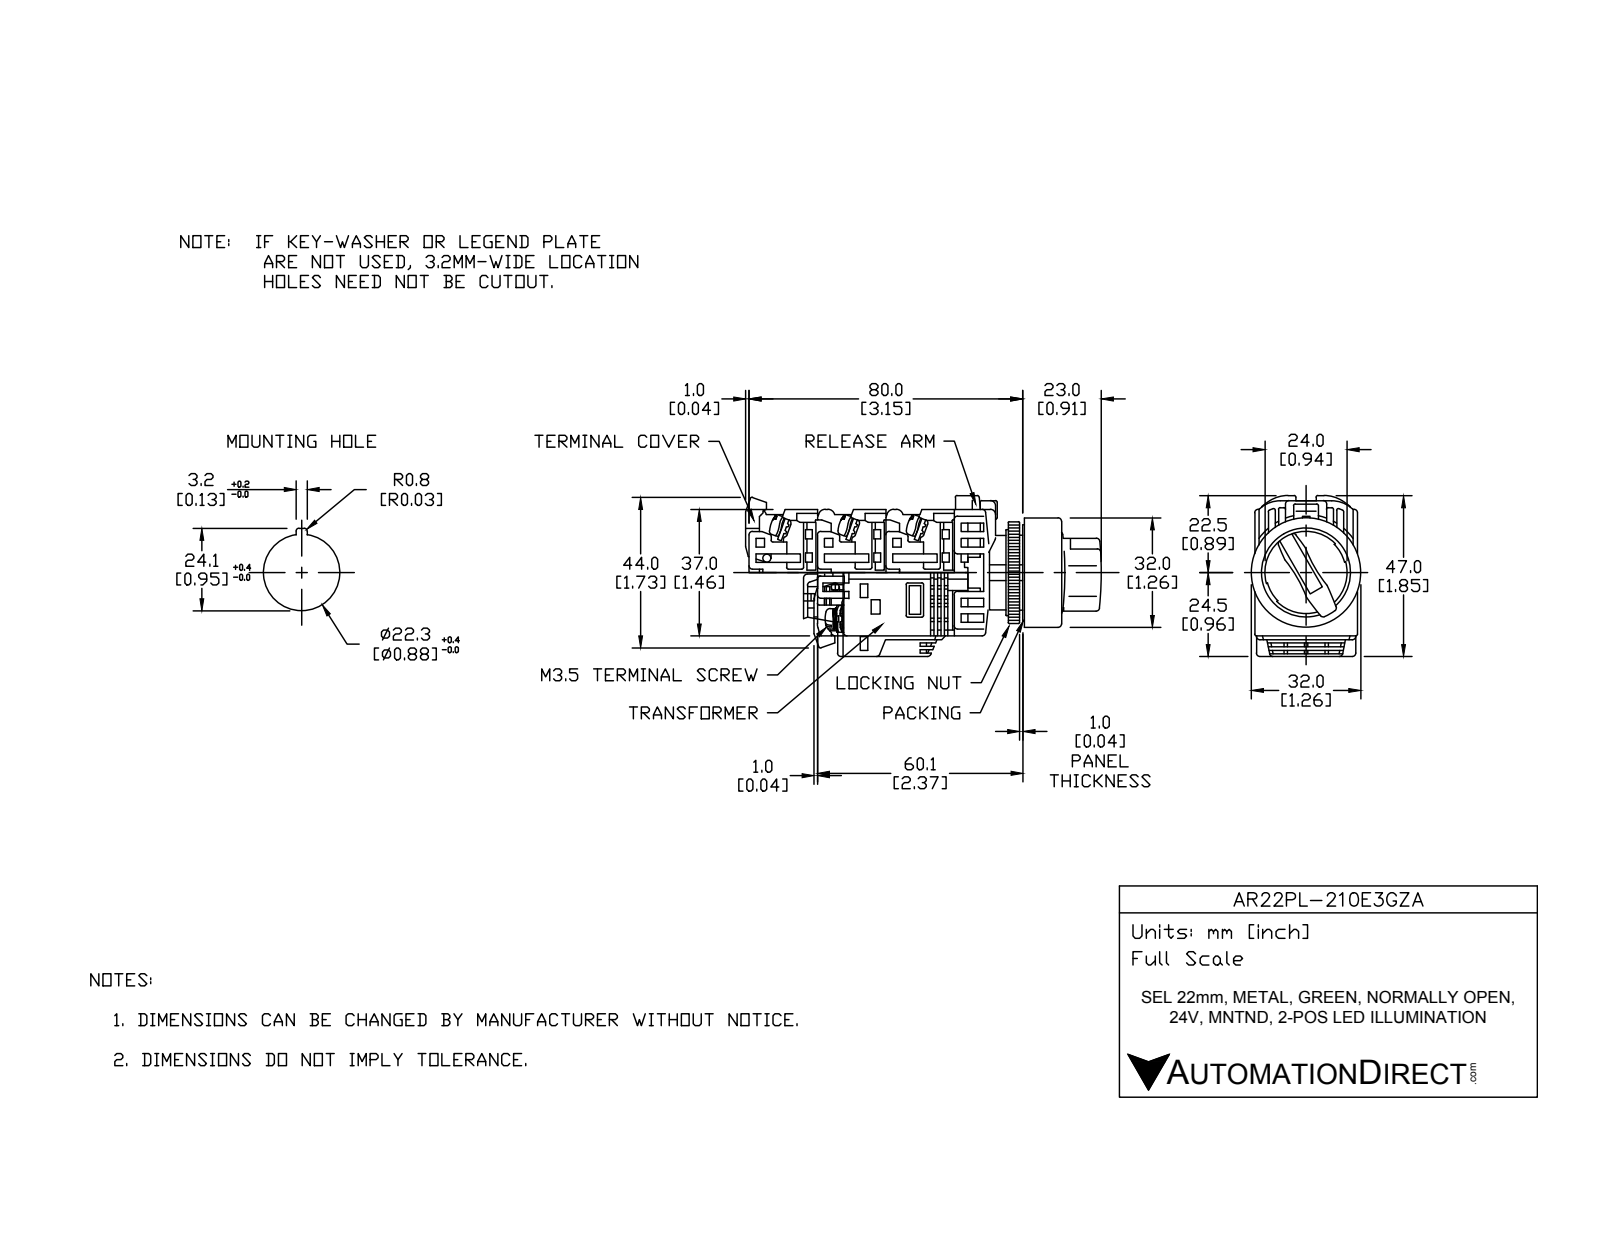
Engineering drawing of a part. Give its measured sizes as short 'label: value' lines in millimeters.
name: AR22PL-210E3GZA
written by: SolidWorks 2017 (AUTOMOTIVE_DESIGN)
unit: mm
bodies: 18 solids, 462 faces (317 planar, 118 cylindrical, 27 other)
size: 64.5 × 43.81 × 32
volume: 38 531 mm³; area: 24 831 mm²
holes: 1× ⌀21.8, 1× ⌀22, 1× ⌀25, 1× ⌀31
bosses: 4× ⌀5, 1× ⌀32, 1× ⌀30.5, 1× ⌀29.8, 1× ⌀24, 1× ⌀21.75, 1× ⌀17
rounds: 39× R0.5, 8× R1.75, 6× R1, 4× R5, 2× R4, 1× R12, 1× R16.59, 1× R17.59
face distances: 1, 18, 3, 28.5, 48.5, 20, 29, 0.5, 2, 31
